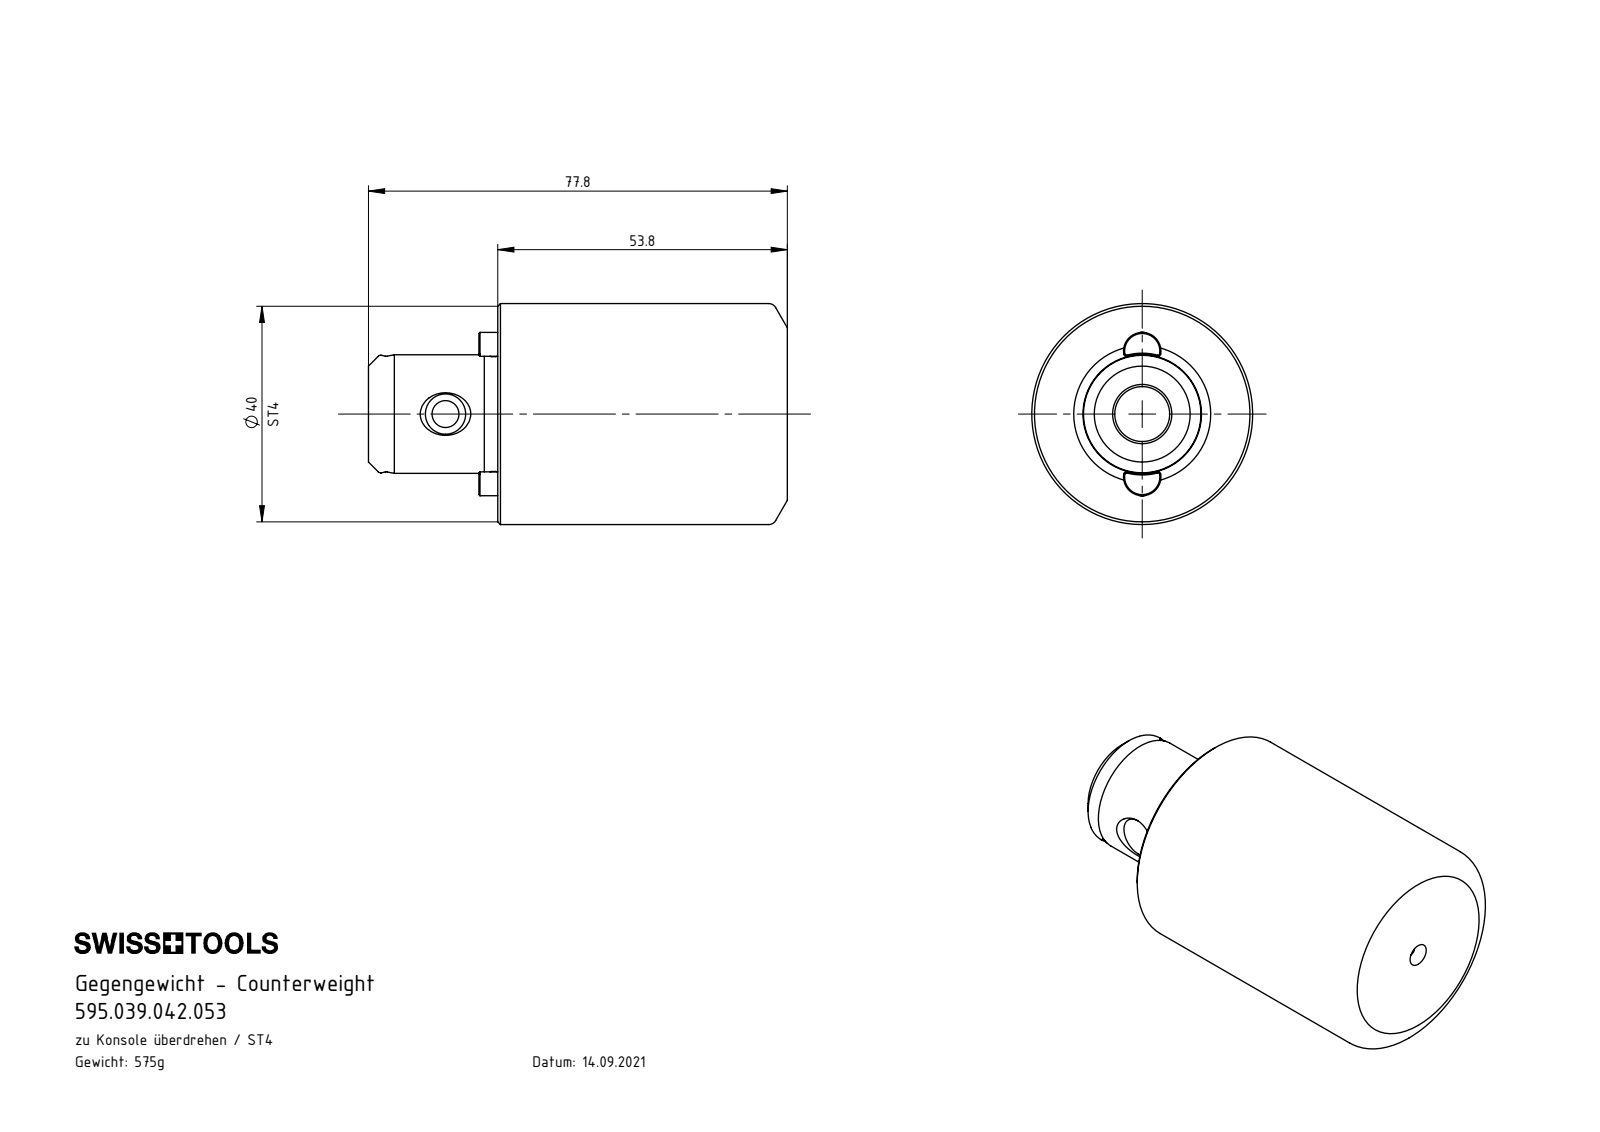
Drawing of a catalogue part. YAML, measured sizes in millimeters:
part_name: "ST4-ER2.001.009_A; CWF-ST4.041.053_A; CWF.ST4.041.053"
step_written_by: "SolidWorks 2017 (AUTOMOTIVE_DESIGN)"
units: millimeters
bodies: {solids: 3, faces: 63, planar: 9, cylindrical: 19, other: 35}
overall_size: [77.75, 41, 41]
volume: 73280
surface_area: 13600
round_holes:
  - {diameter: 3.5, count: 2}
  - {diameter: 2, count: 1}
  - {diameter: 5, count: 1}
  - {diameter: 10.2, count: 1}
round_bosses_or_shafts:
  - {diameter: 41, count: 1}
  - {diameter: 22, count: 1}
  - {diameter: 21.8, count: 1}
  - {diameter: 21.3, count: 1}
partial_cylinders:
  - {radius: 0.5, count: 4}
  - {radius: 3.48, count: 2}
  - {radius: 11.05, count: 2}
face_to_face_distances: [53.75, 24, 77.75, 20.5, 3.5, 57.25, 29, 8.5, 5, 48.75]
hole_center_spacings: [13.2, 26.4]
